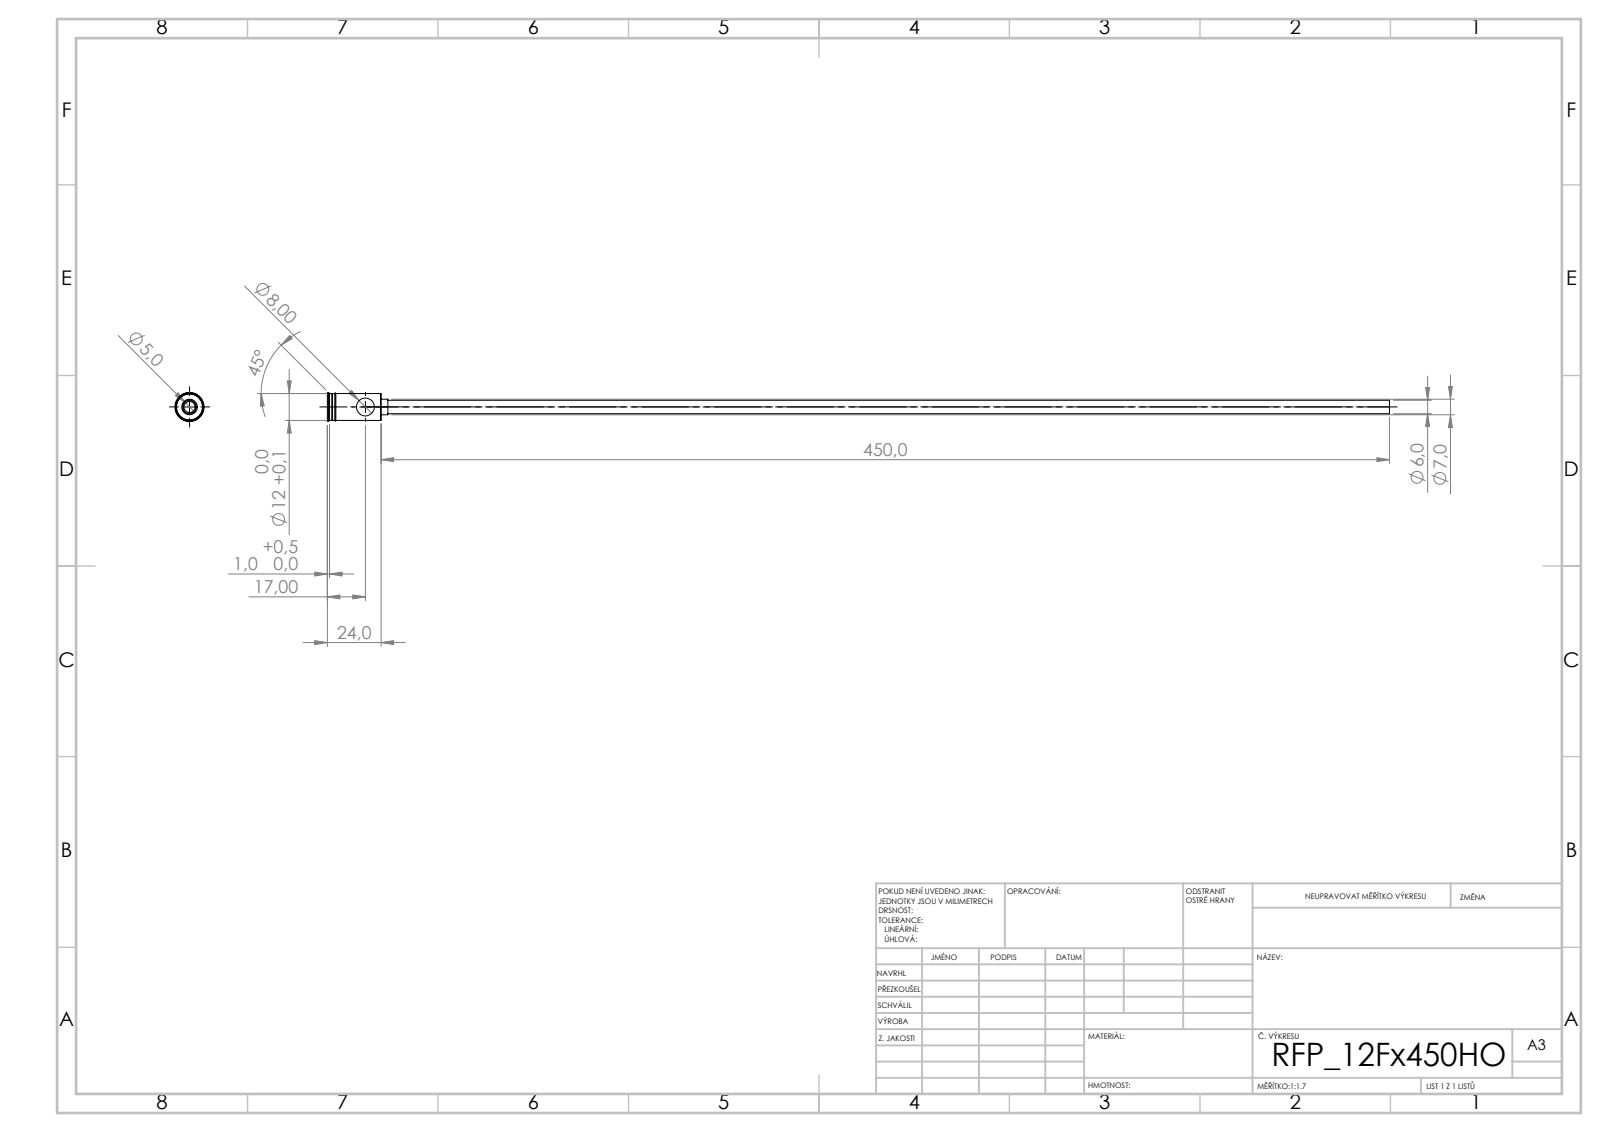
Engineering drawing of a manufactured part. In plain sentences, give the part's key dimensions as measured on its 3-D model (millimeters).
Its 3-D file was written by "SolidWorks 2019 (CONFIG_CONTROL_DESIGN)". It is 1 solid with 44 faces: 20 planar, 16 cylindrical and 8 other. Overall it measures 474 by 13 by 13 millimeters. Its volume is 5 924 cubic millimeters and its surface area 16 967 square millimeters. Round holes: 1 of diameter 5, 1 of diameter 8. Round bosses or shafts: 1 of diameter 13, 1 of diameter 12, 1 of diameter 7, 1 of diameter 6. The main face-to-face distances are 24, 22, 2, 7.4, 21.7, 2.3, 3, 24.7, 25, 27.
